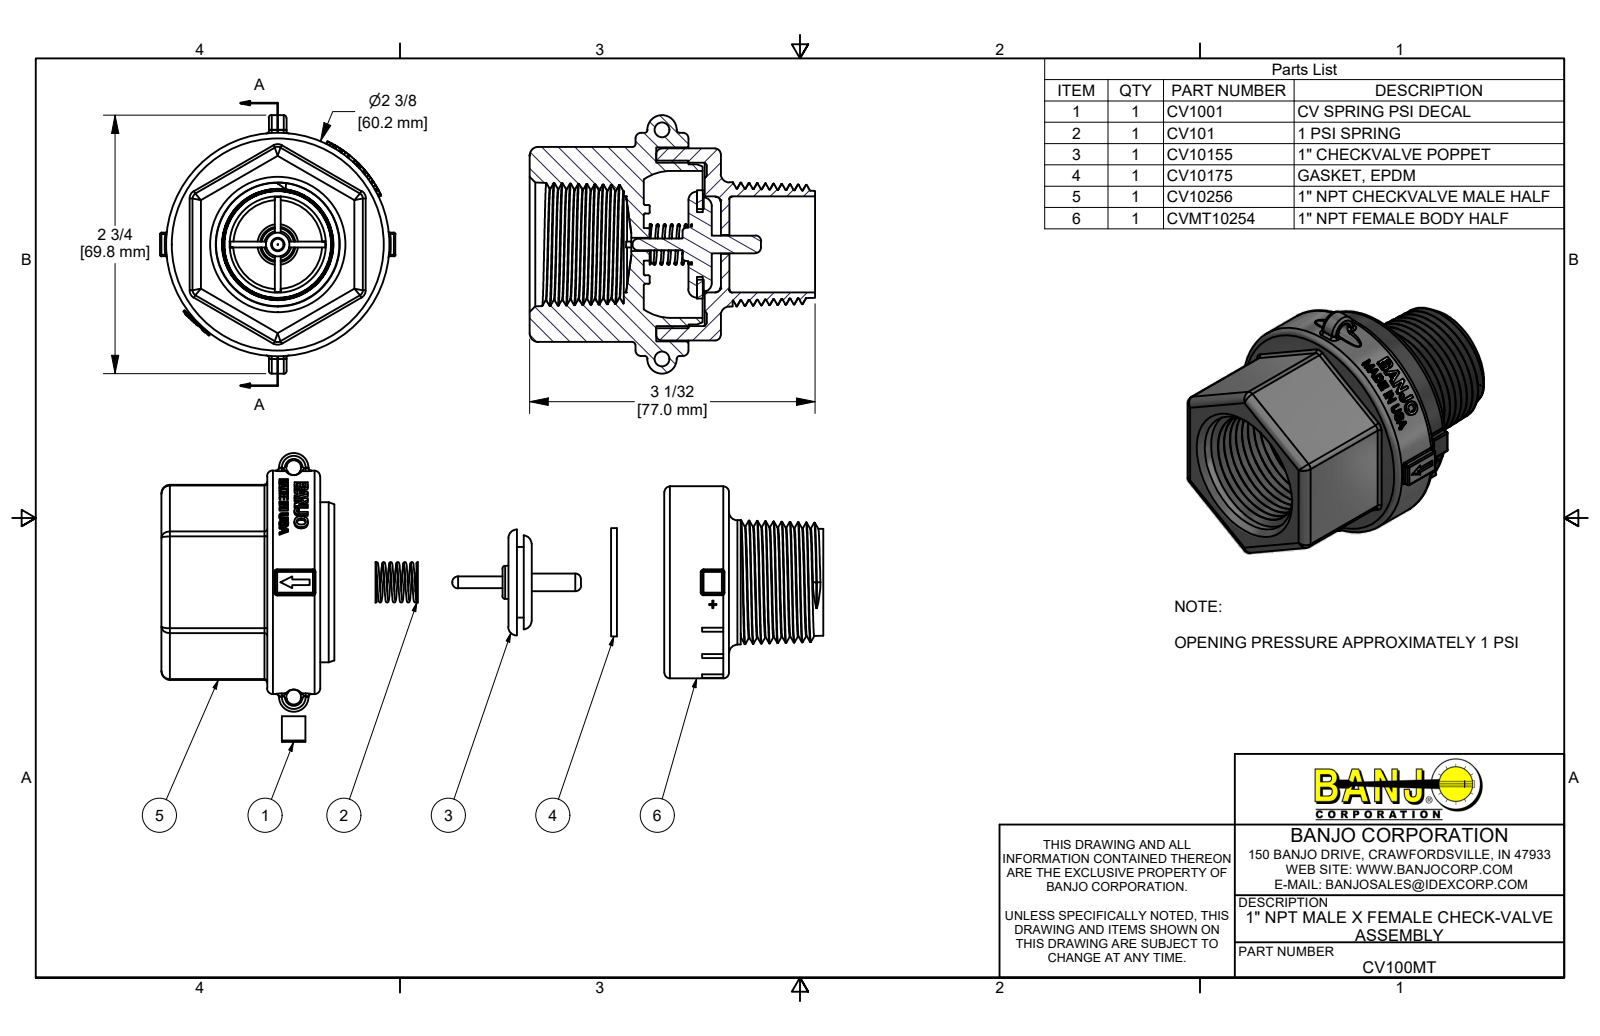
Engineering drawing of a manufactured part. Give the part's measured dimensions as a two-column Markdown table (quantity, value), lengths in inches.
| quantity | value |
| --- | --- |
| part name | CV100MT; CV10256; CVMT10254; CVMT10254X (+4 more) |
| STEP written by | Autodesk Inventor 2019 (AUTOMOTIVE_DESIGN) |
| units | inches |
| bodies | 6 solids, 883 faces (305 planar, 178 cylindrical, 400 other) |
| overall size | 21.293 × 2.747 × 2.5 |
| volume | 4.676 in³ |
| surface area | 377.1 in² |
| round holes (diameter × count) | 0.156 × 2, 0.14 × 1, 0.2 × 1, 0.687 × 1, 1.02 × 1, 1.561 × 1, 1.735 × 1, 2.06 × 1 |
| round bosses / shafts (diameter × count) | 2.372 × 1, 2.04 × 1, 1.78 × 1, 1.7 × 1, 1.32 × 1, 1.15 × 1, 0.75 × 1, 0.187 × 1 |
| partial cylindrical surfaces (radius × count) | 0.015 × 56, 0.03 × 30, 0.06 × 6, 0.09 × 6, 0.156 × 2, 0.125 × 1, 0.15 × 1, 0.172 × 1 |
| main face-to-face distances | 1.81, 0.344, 0.344, 0.688, 0.433, 0.254, 0.219, 0.652, 0.907, 0.563 |
| hole center spacings | 2.435 |
